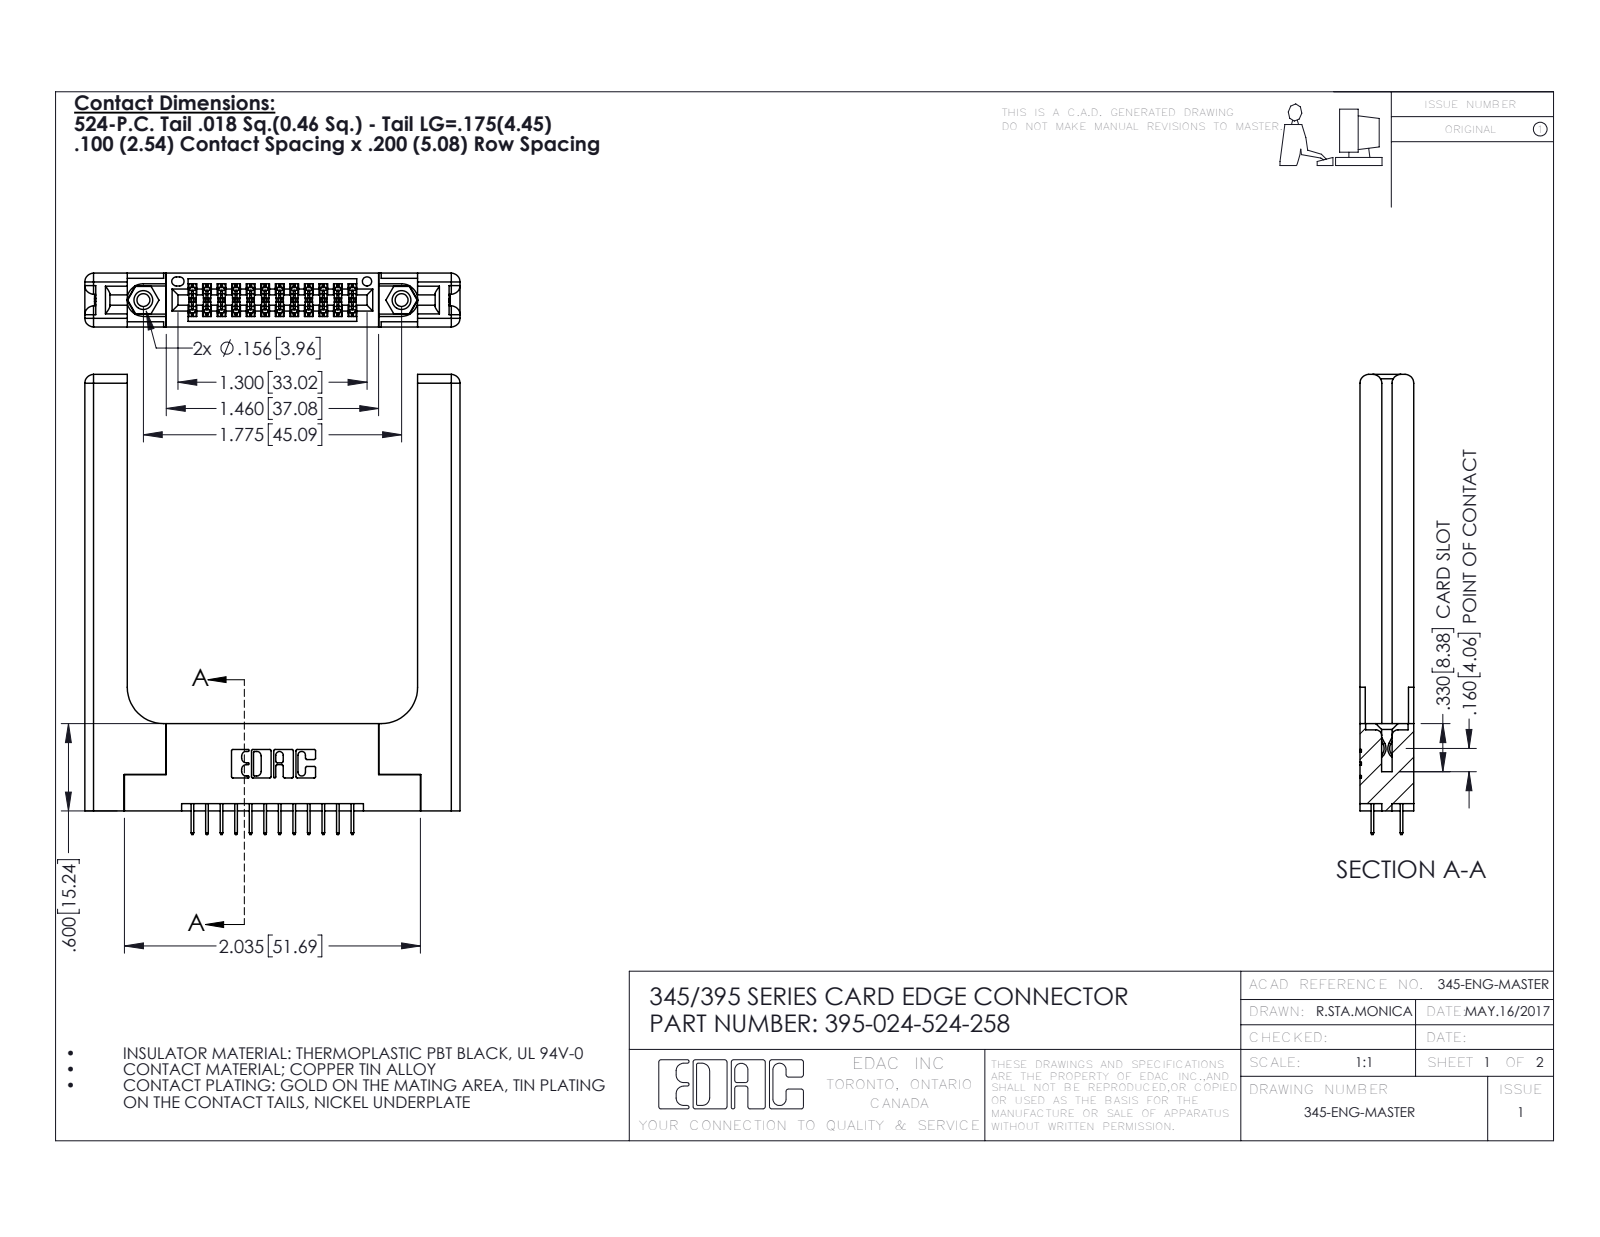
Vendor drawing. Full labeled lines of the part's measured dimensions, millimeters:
Part name (STEP PRODUCT): 345-292-001_345-293-124; 395-024-524-258; 345 Part_Flush Mounting Lugs - 0.156 Dia-TH; 345-250-001_345-250-001-102 (+1 more)
STEP written by: SolidWorks 2016 (CONFIG_CONTROL_DESIGN)
Units: millimetres
Bodies: 29 solids, 1678 faces (1164 planar, 454 cylindrical, 60 other)
Overall size (bounding box): 80.3 × 65.5 × 9.4
Volume: 14 500 mm³ · Surface area: 13 320 mm²
Round holes (diameter × count): ⌀2.3 ×2, ⌀3.2 ×2, ⌀4 ×2, ⌀1.6 ×1
Round bosses / shafts (diameter × count): ⌀3.9 ×2
Partial cylindrical surfaces — rounded edges, fillets, slot ends (radius × count): R0.2 ×36, R0.3 ×22, R1.5 ×16, R0.2 ×6, R0.8 ×6, R0.7 ×3, R0.4 ×2, R0.5 ×2
Main face-to-face distances: 9.4, 1.8, 2, 3.8, 3.8, 7.6, 5.6, 5.1, 5.7, 50.7
Hole centre spacings: 6.9, 39.2, 45.1
